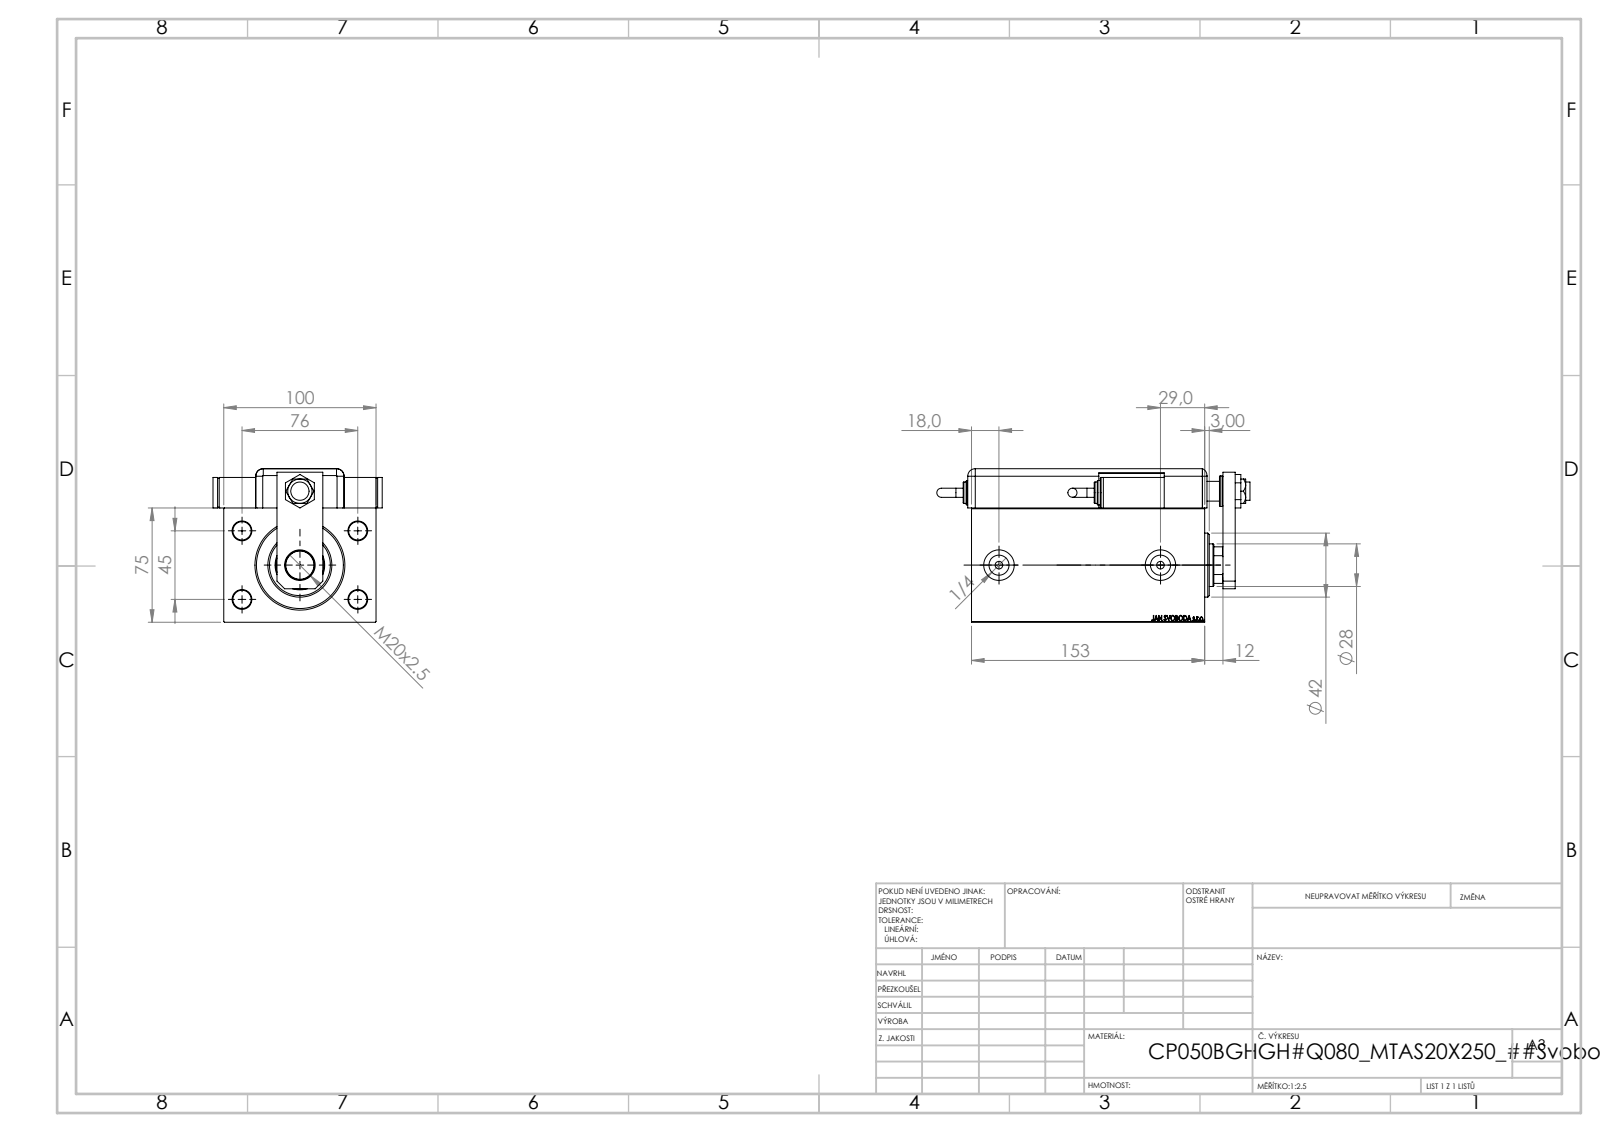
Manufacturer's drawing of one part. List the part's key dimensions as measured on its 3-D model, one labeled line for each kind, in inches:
Part name (STEP PRODUCT): SWITCH_Q_FRONT_BACK; V450CM_VC_B; ZARAZKA_Q; KRYT (+7 more)
STEP written by: SolidWorks 2019 (CONFIG_CONTROL_DESIGN)
Units: inches
Bodies: 13 solids, 1268 faces (608 planar, 111 cylindrical, 549 other)
Overall size (bounding box): 8.089 × 4.37 × 3.969
Volume: 72.31 in³ · Surface area: 302.6 in²
Round holes (diameter × count): ⌀0.472 ×5, ⌀0.787 ×3, ⌀0.157 ×2, ⌀0.197 ×2, ⌀0.315 ×2, ⌀0.518 ×2, ⌀0.512 ×1, ⌀0.551 ×1, ⌀0.728 ×1, ⌀1.102 ×1, ⌀1.24 ×1, ⌀1.28 ×1
Round bosses / shafts (diameter × count): ⌀0.787 ×3, ⌀0.63 ×2, ⌀0.551 ×2, ⌀0.236 ×2, ⌀1.654 ×1
Partial cylindrical surfaces — rounded edges, fillets, slot ends (radius × count): R0.197 ×9, R0.394 ×1, R0.531 ×1
Main face-to-face distances: 2.953, 0.118, 3.937, 1.016, 3.969, 0.945, 0.551, 3.85, 0.898, 6.024
Hole centre spacings: 1.739, 1.772, 1.813, 2.992, 3.17, 3.477, 0.787, 1.909
